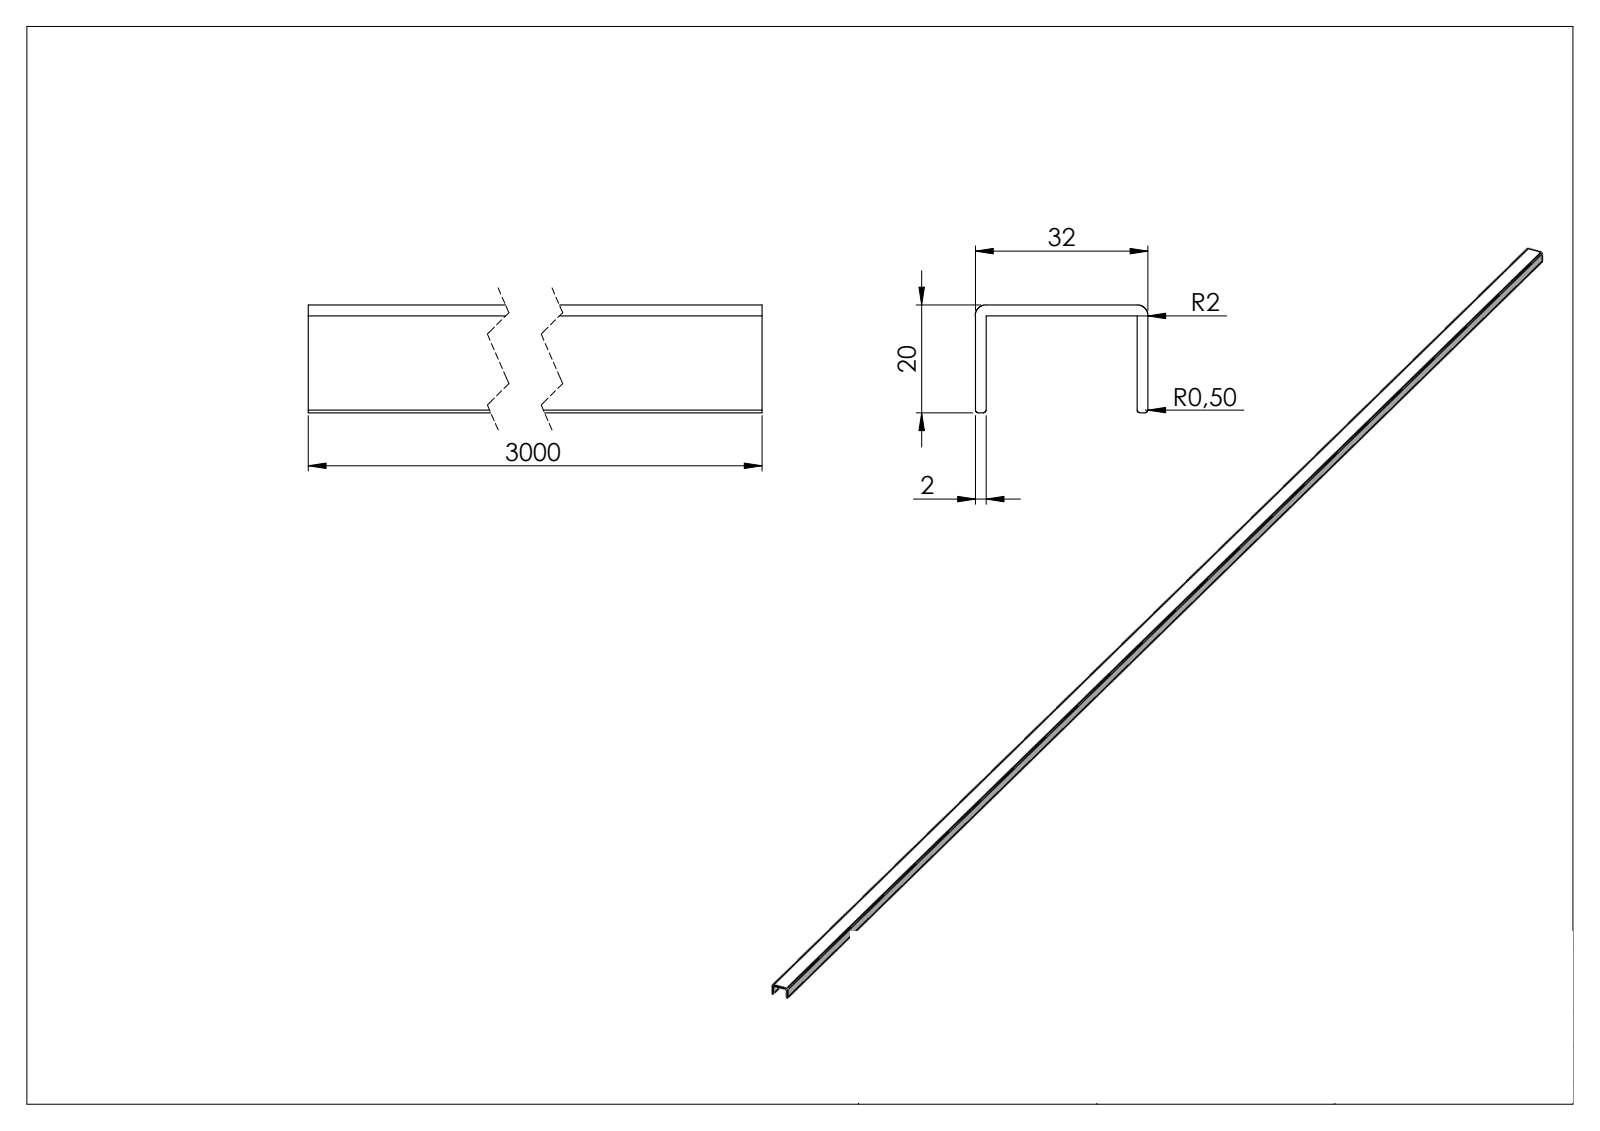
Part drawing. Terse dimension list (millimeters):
name: 80531-ALU-3M
written by: SolidWorks 2015 (CONFIG_CONTROL_DESIGN)
unit: mm
bodies: 1 solid, 283 faces (151 planar, 6 cylindrical, 126 other)
size: 3000 × 32 × 20
volume: 402 205 mm³; area: 412 554 mm²
rounds: 4× R0.5, 2× R2
face distances: 2, 30, 32, 28, 18, 20, 3000, 1.9, 28.1, 30.1
